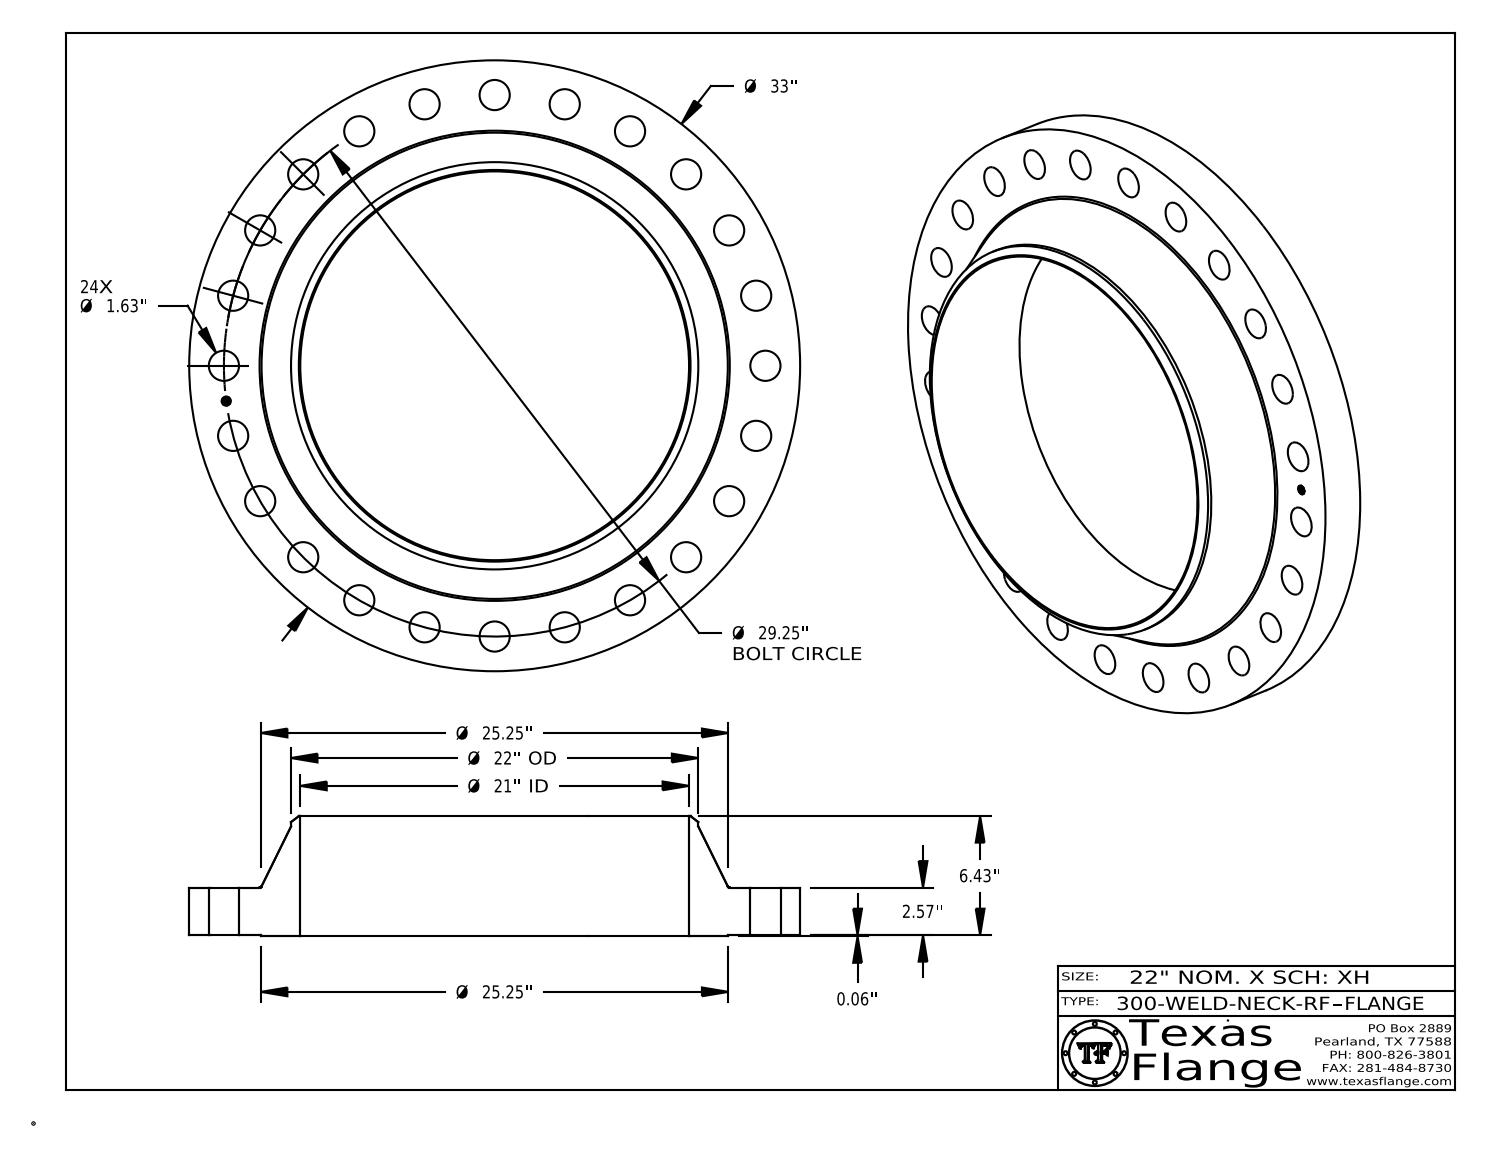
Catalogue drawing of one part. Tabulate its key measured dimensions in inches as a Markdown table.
| quantity | value |
| --- | --- |
| part name | 300-WELD-NECK-RF |
| STEP written by | CATIA V5 STEP AP214 (AUTOMOTIVE_DESIGN) |
| units | inches |
| bodies | 1 solid, 451 faces (369 planar, 76 cylindrical, 6 other) |
| overall size | 33 × 33 × 6.493 |
| volume | 1 509 in³ |
| surface area | 2 108 in² |
| round holes (diameter × count) | 1.63 × 24, 0.495 × 1, 21 × 1 |
| round bosses / shafts (diameter × count) | 0.03 × 8, 33 × 1, 25.25 × 1, 22 × 1, 0.39 × 1 |
| main face-to-face distances | 2.57, 0.063, 2.633, 6.493, 6.43, 3.86, 2.618, 2.555, 0.015, 3.875 |
| hole center spacings | 14.625, 27.024, 7.57, 20.683, 3.818, 11.194, 17.806, 23.206 |
